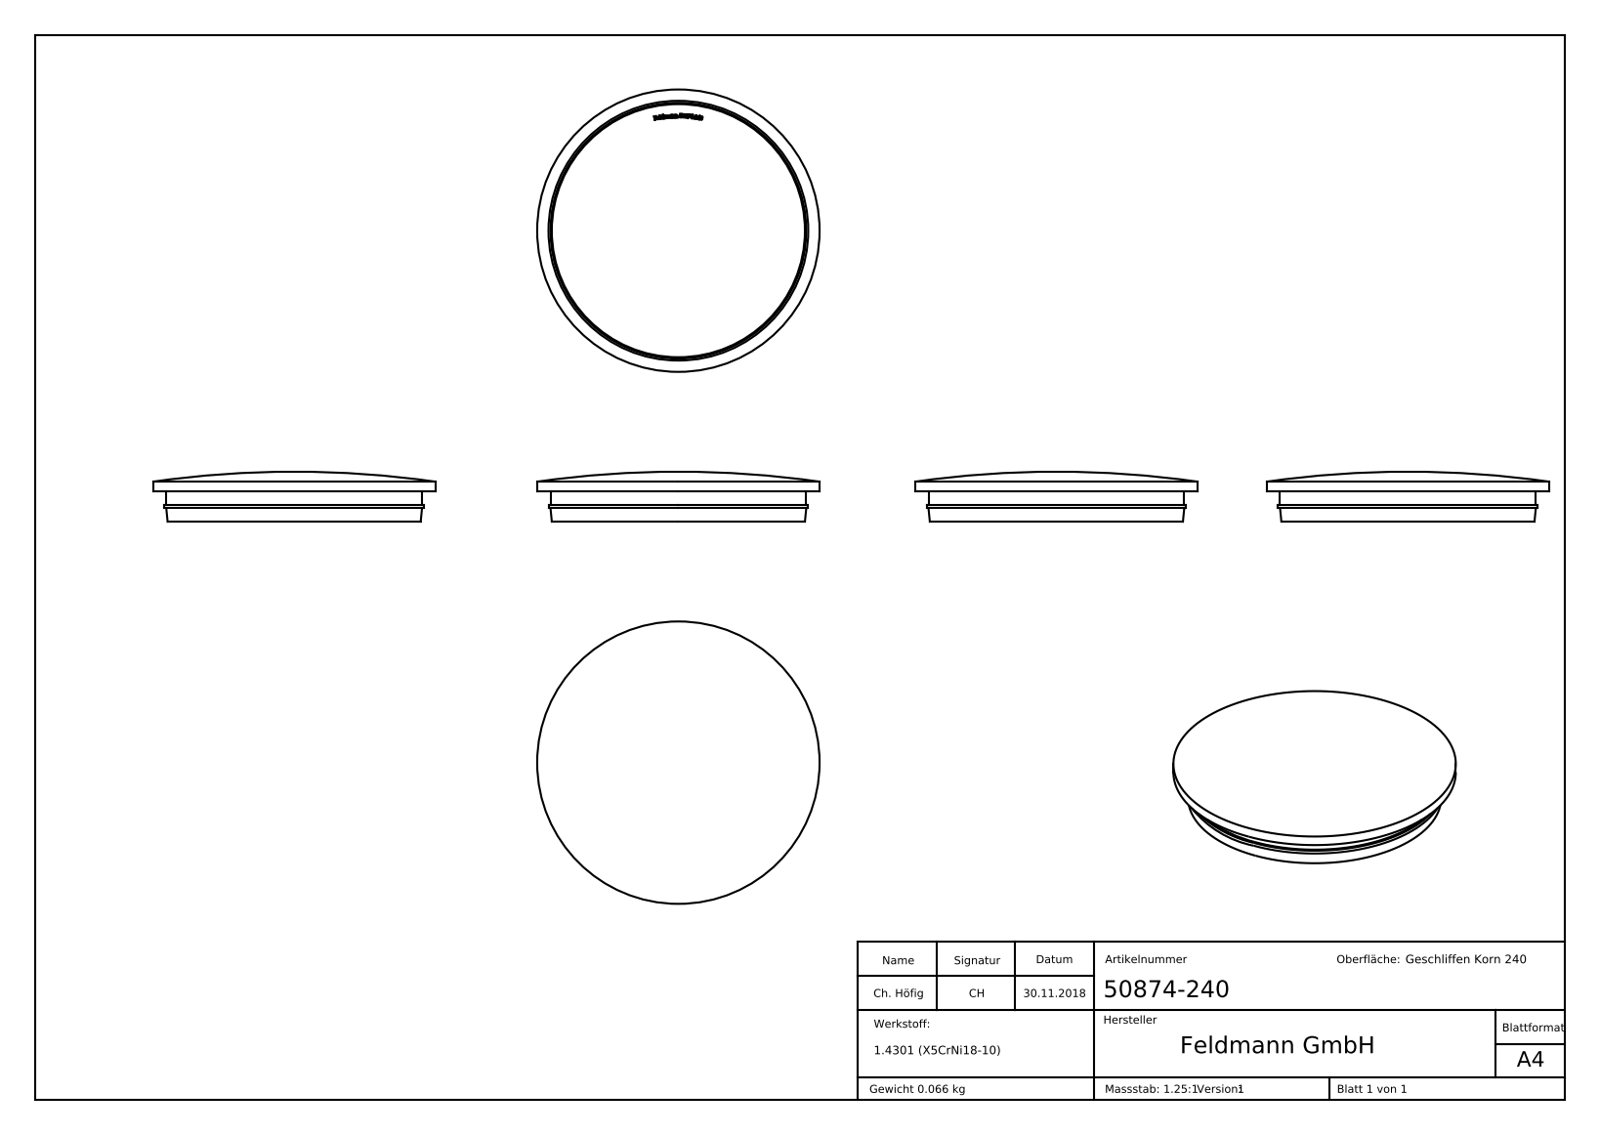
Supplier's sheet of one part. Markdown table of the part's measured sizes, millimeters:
| quantity | value |
| --- | --- |
| part name | 50874-240 |
| STEP written by | SolidWorks 2015 (CONFIG_CONTROL_DESIGN) |
| units | millimeters |
| bodies | 1 solid, 239 faces (132 planar, 6 cylindrical, 101 other) |
| overall size | 42.4 × 42.4 × 7.5 |
| volume | 8 384 mm³ |
| surface area | 3 643 mm² |
| round bosses / shafts (diameter × count) | 42.4 × 1, 39 × 1, 38.4 × 1 |
| main face-to-face distances | 4.5, 2, 2.5, 0.5, 1.5, 4, 0.54, 0.49, 0.31, 0.33 |
